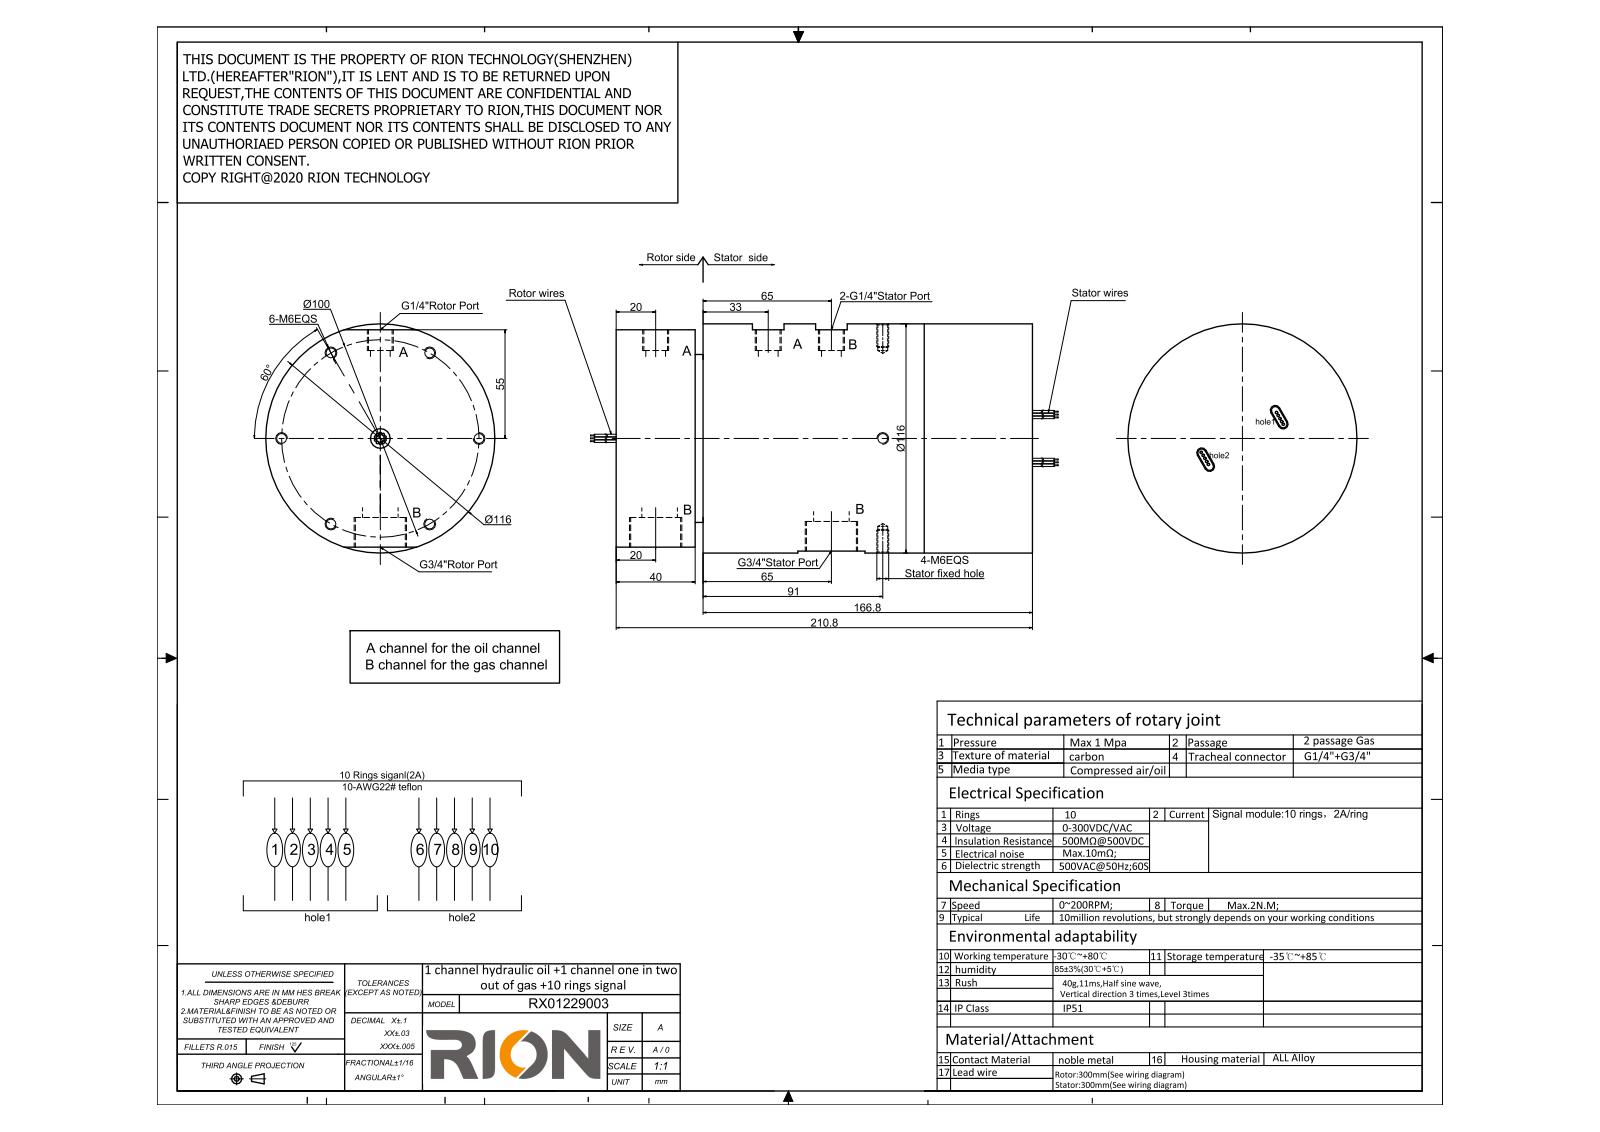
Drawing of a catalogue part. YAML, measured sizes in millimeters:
step_written_by: "SolidWorks 2014 (CONFIG_CONTROL_DESIGN)"
units: millimeters
bodies: {solids: 1, faces: 157, planar: 42, cylindrical: 85, other: 30}
overall_size: [252.8, 116, 116]
volume: 2175000
surface_area: 115335
round_holes:
  - {diameter: 5, count: 8}
  - {diameter: 11.8, count: 3}
  - {diameter: 24.5, count: 2}
  - {diameter: 10, count: 1}
round_bosses_or_shafts:
  - {diameter: 1.3, count: 20}
  - {diameter: 116, count: 1}
  - {diameter: 85, count: 1}
partial_cylinders:
  - {radius: 2, count: 4}
face_to_face_distances: [210.8, 44, 166.8, 4, 40, 170.8, 1, 110, 109, 111]
hole_center_spacings: [50, 86.6, 100, 26, 32, 57, 58, 89]
